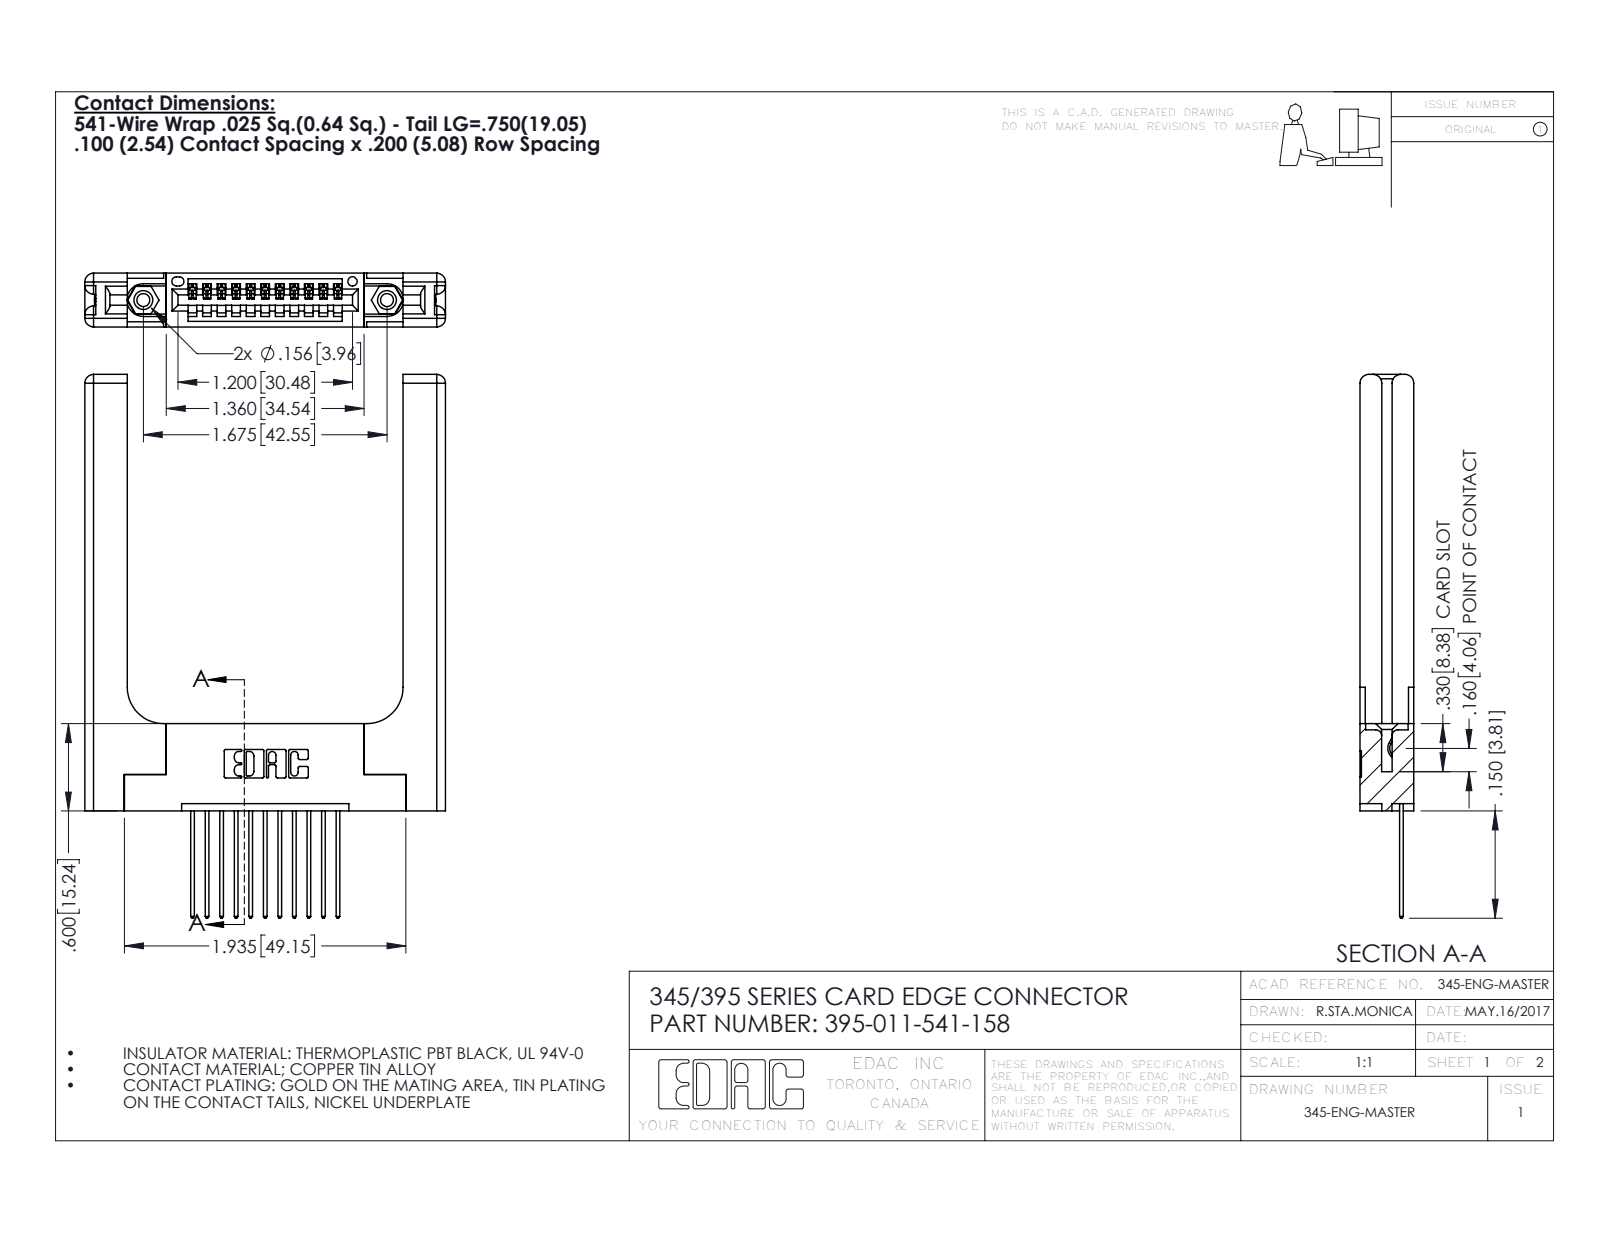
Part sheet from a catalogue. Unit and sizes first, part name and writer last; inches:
Units: inches
Overall size (bounding box): 3.737 × 2.479 × 0.37
Round holes (diameter × count): ⌀0.089 ×2, ⌀0.125 ×2, ⌀0.156 ×2, ⌀0.064 ×1
Round bosses / shafts (diameter × count): ⌀0.155 ×2
Partial cylindrical surfaces — rounded edges, fillets, slot ends (radius × count): R0.006 ×22, R0.01 ×22, R0.01 ×22, R0.06 ×16, R0.007 ×6, R0.031 ×6, R0.026 ×3, R0.03 ×2
Main face-to-face distances: 0.37, 0.072, 0.15, 0.298, 0.22, 0.077, 0.148, 0.2, 1.896, 0.098
Hole centre spacings: 0.27, 1.443, 1.675
Volume: 0.871 in³ · Surface area: 19.77 in²
Bodies: 16 solids, 1020 faces (668 planar, 292 cylindrical, 60 other)
Part name (STEP PRODUCT): 345-220-058_345-220-058; 345-292-001_345-293-141; 345 Part_Flush Mounting Lugs - 0.156 Dia-TH; 395-011-541-158 (+1 more)
STEP written by: SolidWorks 2016 (CONFIG_CONTROL_DESIGN)
